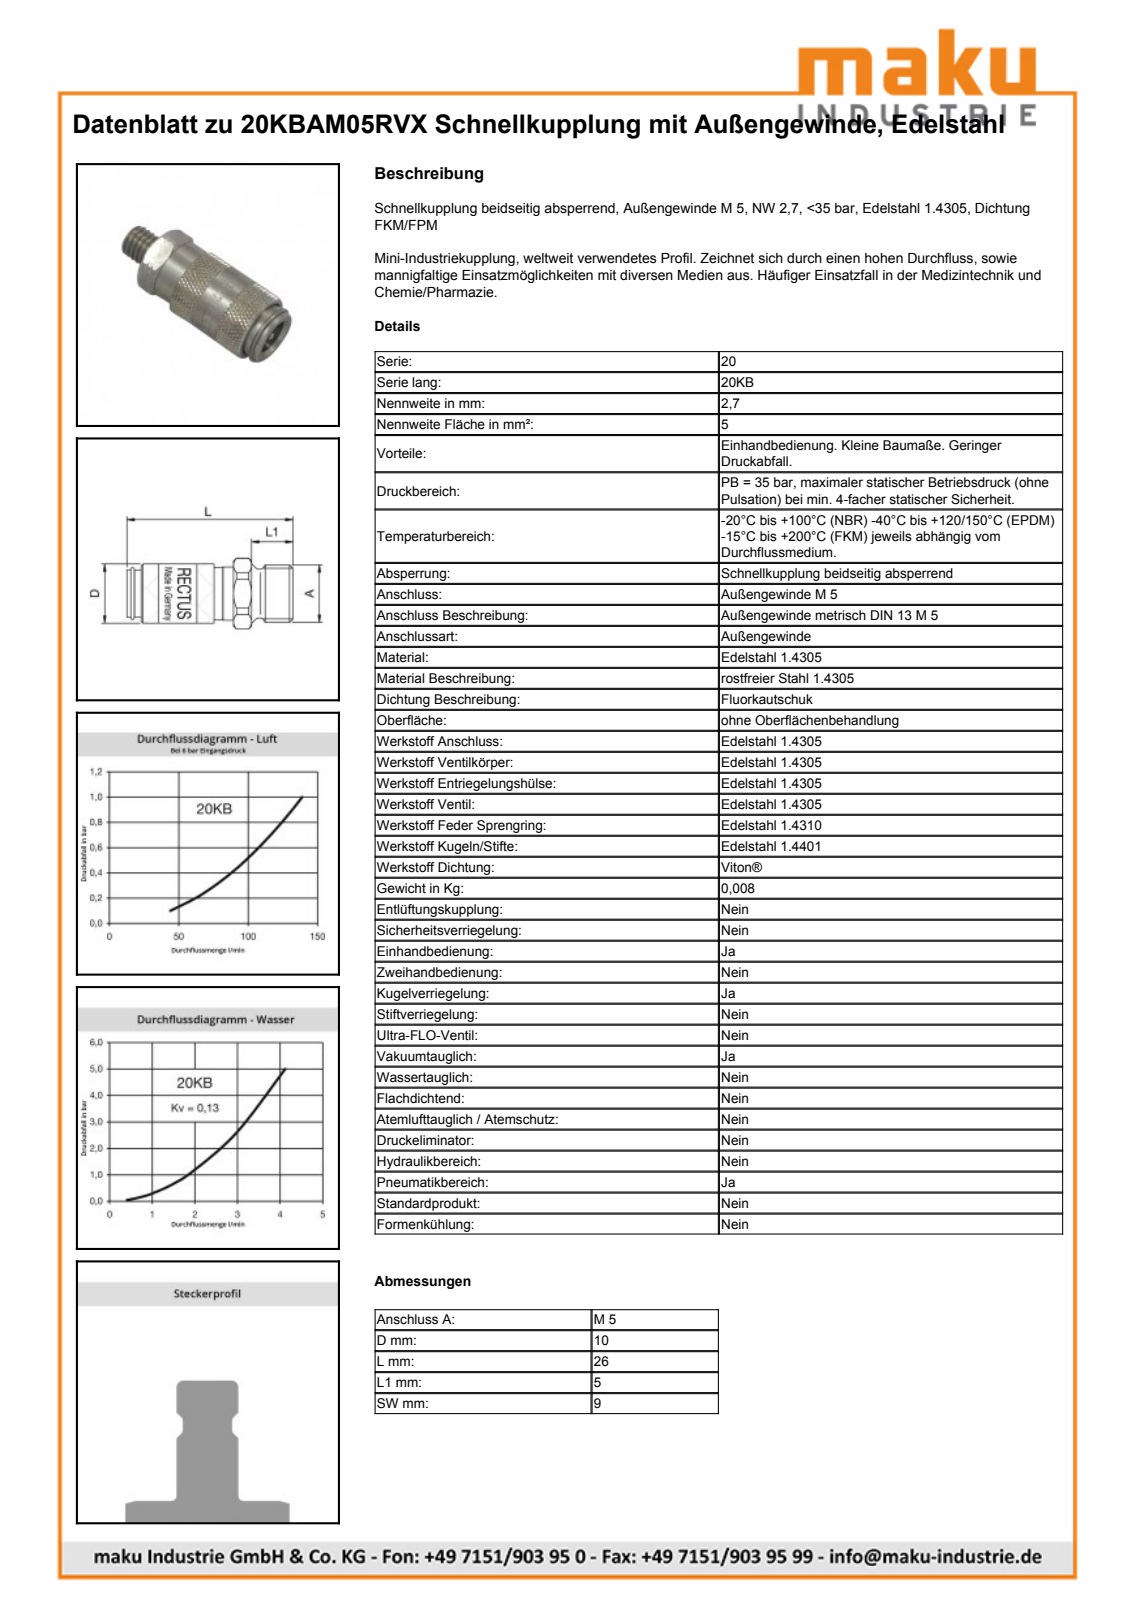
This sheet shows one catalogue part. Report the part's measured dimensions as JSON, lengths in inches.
{"part_name": "D109646", "step_written_by": "Autodesk Inventor 2013 (AUTOMOTIVE_DESIGN)", "units": "inches", "bodies": {"solids": 2, "faces": 408, "planar": 167, "cylindrical": 62, "other": 179}, "overall_size": [1.026, 0.407, 0.407], "volume_in3": 0.092, "surface_area_in2": 2.956, "round_holes": [[0.256, 1], [0.294, 1], [0.319, 1], [0.321, 1], [0.36, 1], [0.362, 1]], "round_bosses_or_shafts": [[0.407, 1], [0.394, 1], [0.354, 1], [0.315, 1], [0.307, 1], [0.291, 1], [0.287, 1], [0.268, 1]], "partial_cylinders_radius": [[0.193, 1], [0.195, 1]], "face_to_face_distances": [0.829, 0.197, 0.354, 0.447, 0.13, 0.094, 0.734, 0.317, 0.579, 0.484]}
